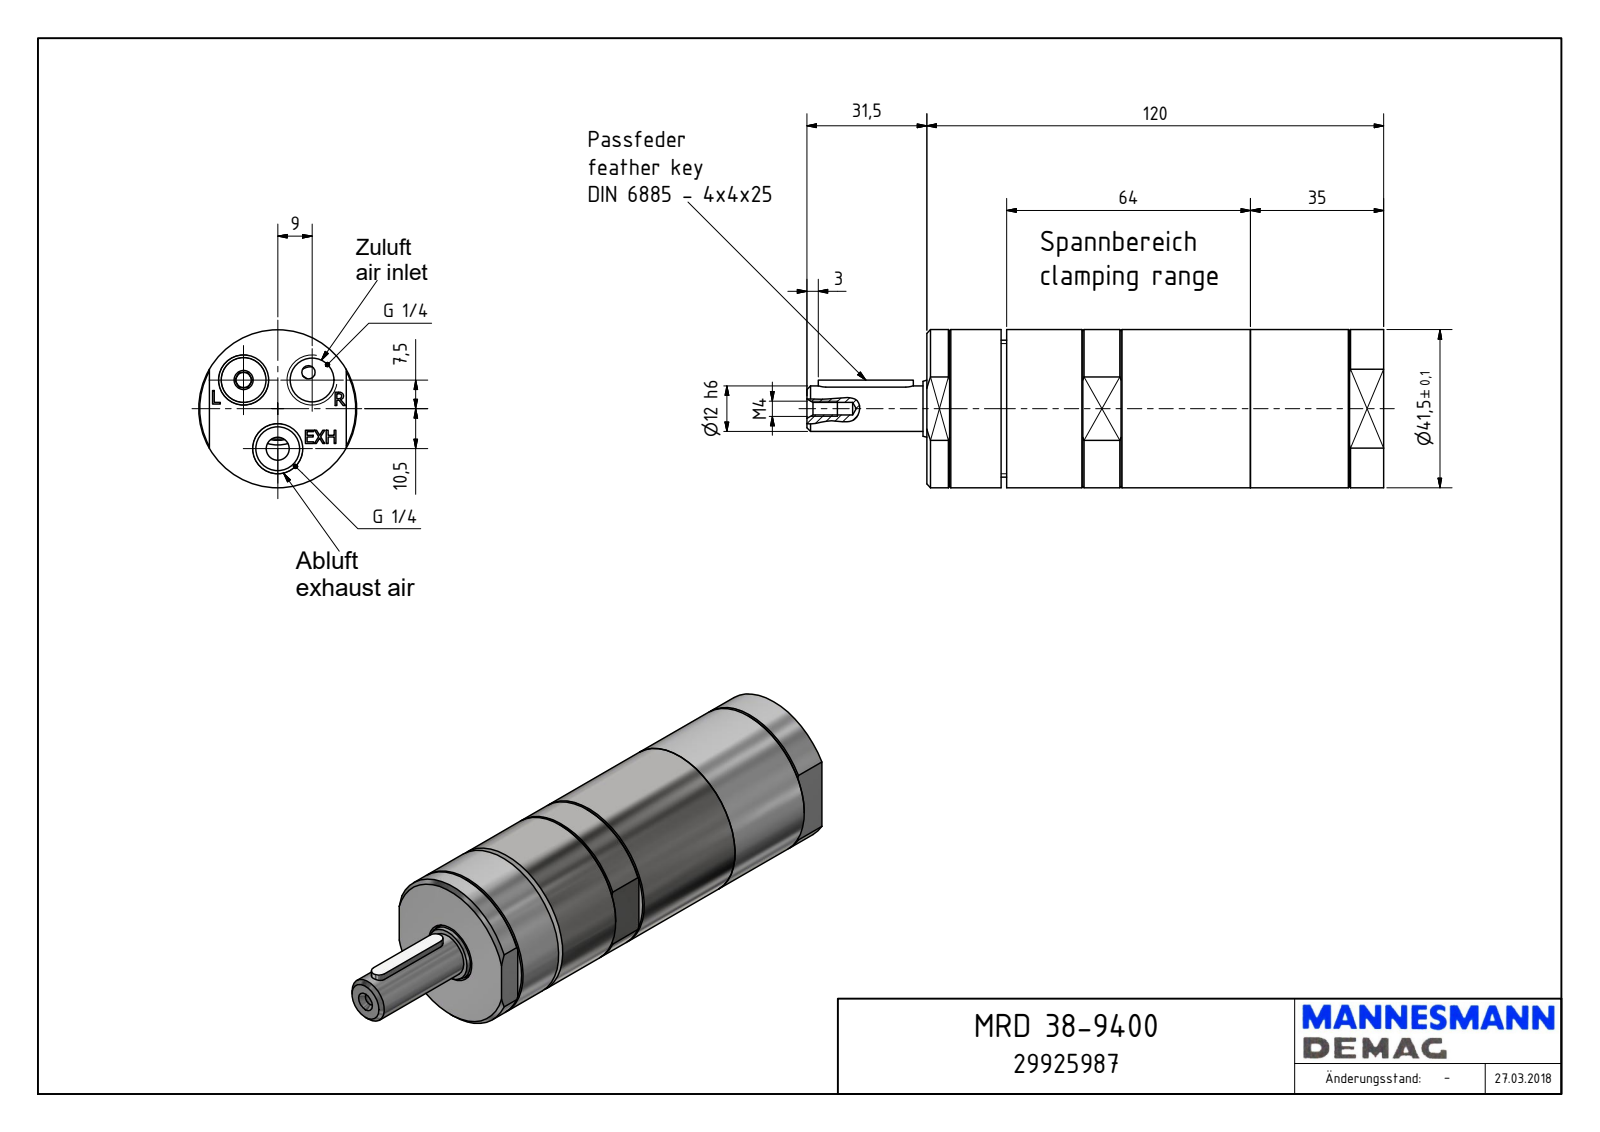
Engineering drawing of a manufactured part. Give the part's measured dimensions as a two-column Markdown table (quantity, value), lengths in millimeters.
| quantity | value |
| --- | --- |
| part name | MRD 38-9400_29925987 |
| STEP written by | Autodesk Inventor 2018 (AUTOMOTIVE_DESIGN) |
| units | millimeters |
| bodies | 1 solid, 152 faces (100 planar, 21 cylindrical, 31 other) |
| overall size | 151.5 × 41.5 × 41.5 |
| volume | 160 373 mm³ |
| surface area | 22 050 mm² |
| round holes (diameter × count) | 11.45 × 3, 3.24 × 1, 4 × 1, 16 × 1 |
| round bosses / shafts (diameter × count) | 41.5 × 1, 36 × 1, 14.95 × 1, 12 × 1 |
| partial cylindrical surfaces (radius × count) | 2 × 2 |
| main face-to-face distances | 120, 1, 21, 37, 99, 100.5, 1.5, 19.5, 14.72, 84.28 |
| hole center spacings | 11.72, 20.12, 10.5, 18 |
